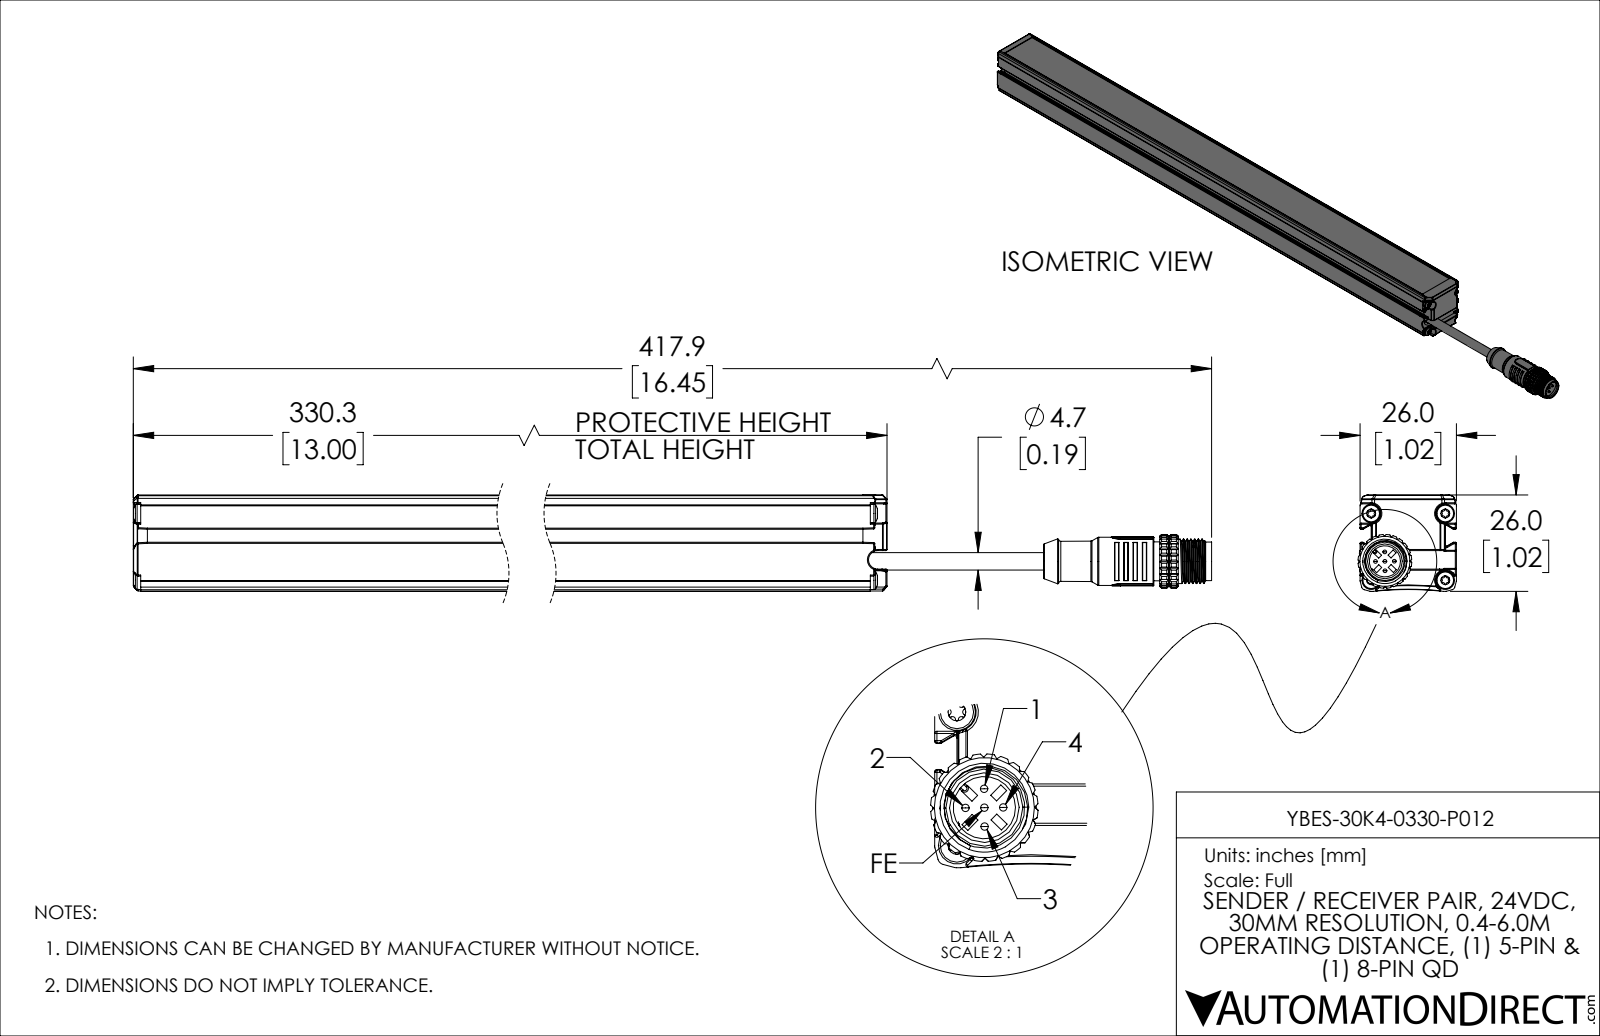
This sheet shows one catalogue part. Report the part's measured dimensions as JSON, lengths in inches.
{"part_name": "YBES-30K4-0330-P012_REV1", "step_written_by": "SolidWorks 2019 (AUTOMOTIVE_DESIGN)", "units": "inches", "bodies": {"solids": 2, "faces": 1937, "planar": 729, "cylindrical": 727, "other": 481}, "overall_size": [16.453, 1.045, 1.024], "volume_in3": 5.008, "surface_area_in2": 138, "round_holes": [[0.094, 4], [0.1, 4], [0.146, 4], [0.197, 4], [0.189, 1], [0.232, 1], [0.331, 1], [0.354, 1], [0.376, 1]], "round_bosses_or_shafts": [[0.039, 5], [0.035, 5], [0.126, 4], [0.098, 4], [0.051, 4], [0.059, 2], [0.531, 1], [0.512, 1]], "partial_cylinders_radius": [[0.008, 153], [0.012, 115], [0.008, 24], [0.015, 24], [0.039, 18], [0.016, 16], [0.006, 10], [0.02, 7]], "face_to_face_distances": [0.118, 0.059, 0.071, 0.835, 1.024, 0.717, 0.047, 0.016, 0.906, 0.189], "hole_center_spacings": [0.709, 0.787, 1.059, 0.248, 0.528, 0.672, 0.819]}
